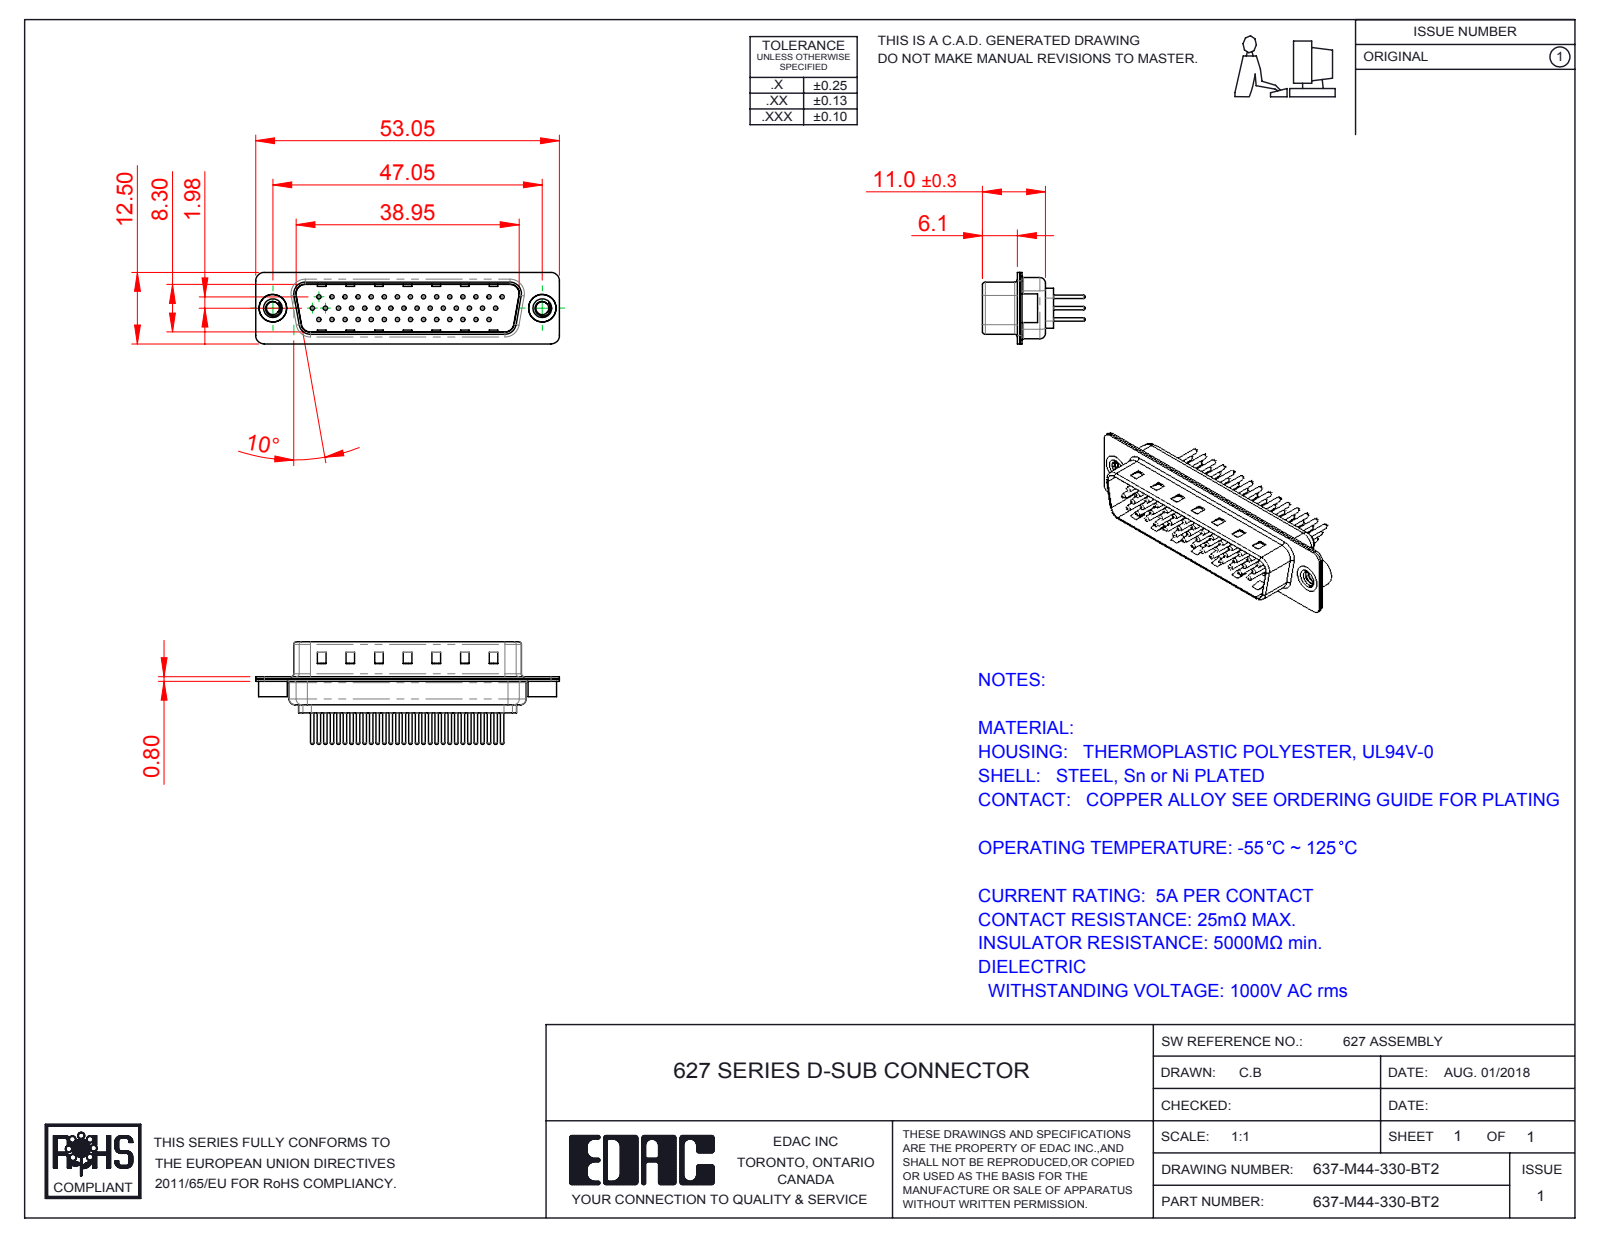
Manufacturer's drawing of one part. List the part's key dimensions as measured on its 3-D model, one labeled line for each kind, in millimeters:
Part name (STEP PRODUCT): 637M Shell Front_44 Contacts; 637M 4-40 Threaded Rivet; 637-M44-330-BT2; 637M Shell Rear_44 Contacts (+4 more)
STEP written by: SolidWorks 2016 (CONFIG_CONTROL_DESIGN)
Units: millimetres
Bodies: 49 solids, 2004 faces (479 planar, 753 cylindrical, 772 other)
Overall size (bounding box): 53.05 × 17.9 × 12.5
Volume: 2 828 mm³ · Surface area: 8 467 mm²
Round holes (diameter × count): ⌀0.75 ×44, ⌀1.6 ×44, ⌀2 ×44, ⌀2.26 ×2, ⌀4 ×2, ⌀4.8 ×2
Round bosses / shafts (diameter × count): ⌀1.5 ×44, ⌀0.6 ×44, ⌀2 ×3, ⌀0.75 ×3, ⌀5 ×2, ⌀4.9 ×2
Partial cylindrical surfaces — rounded edges, fillets, slot ends (radius × count): R1.5 ×16, R2 ×12, R0.5 ×8, R1.6 ×8, R0.25 ×4, R0.6 ×4, R0.65 ×4, R0.9 ×4
Main face-to-face distances: 0.4, 0.8, 9.5, 9.1, 8.7, 9.9, 0.75, 0.35, 1.1, 5.9
Hole centre spacings: 2.28, 3.96, 2.29, 4.57, 8.24, 6.86, 11.43, 14.99
